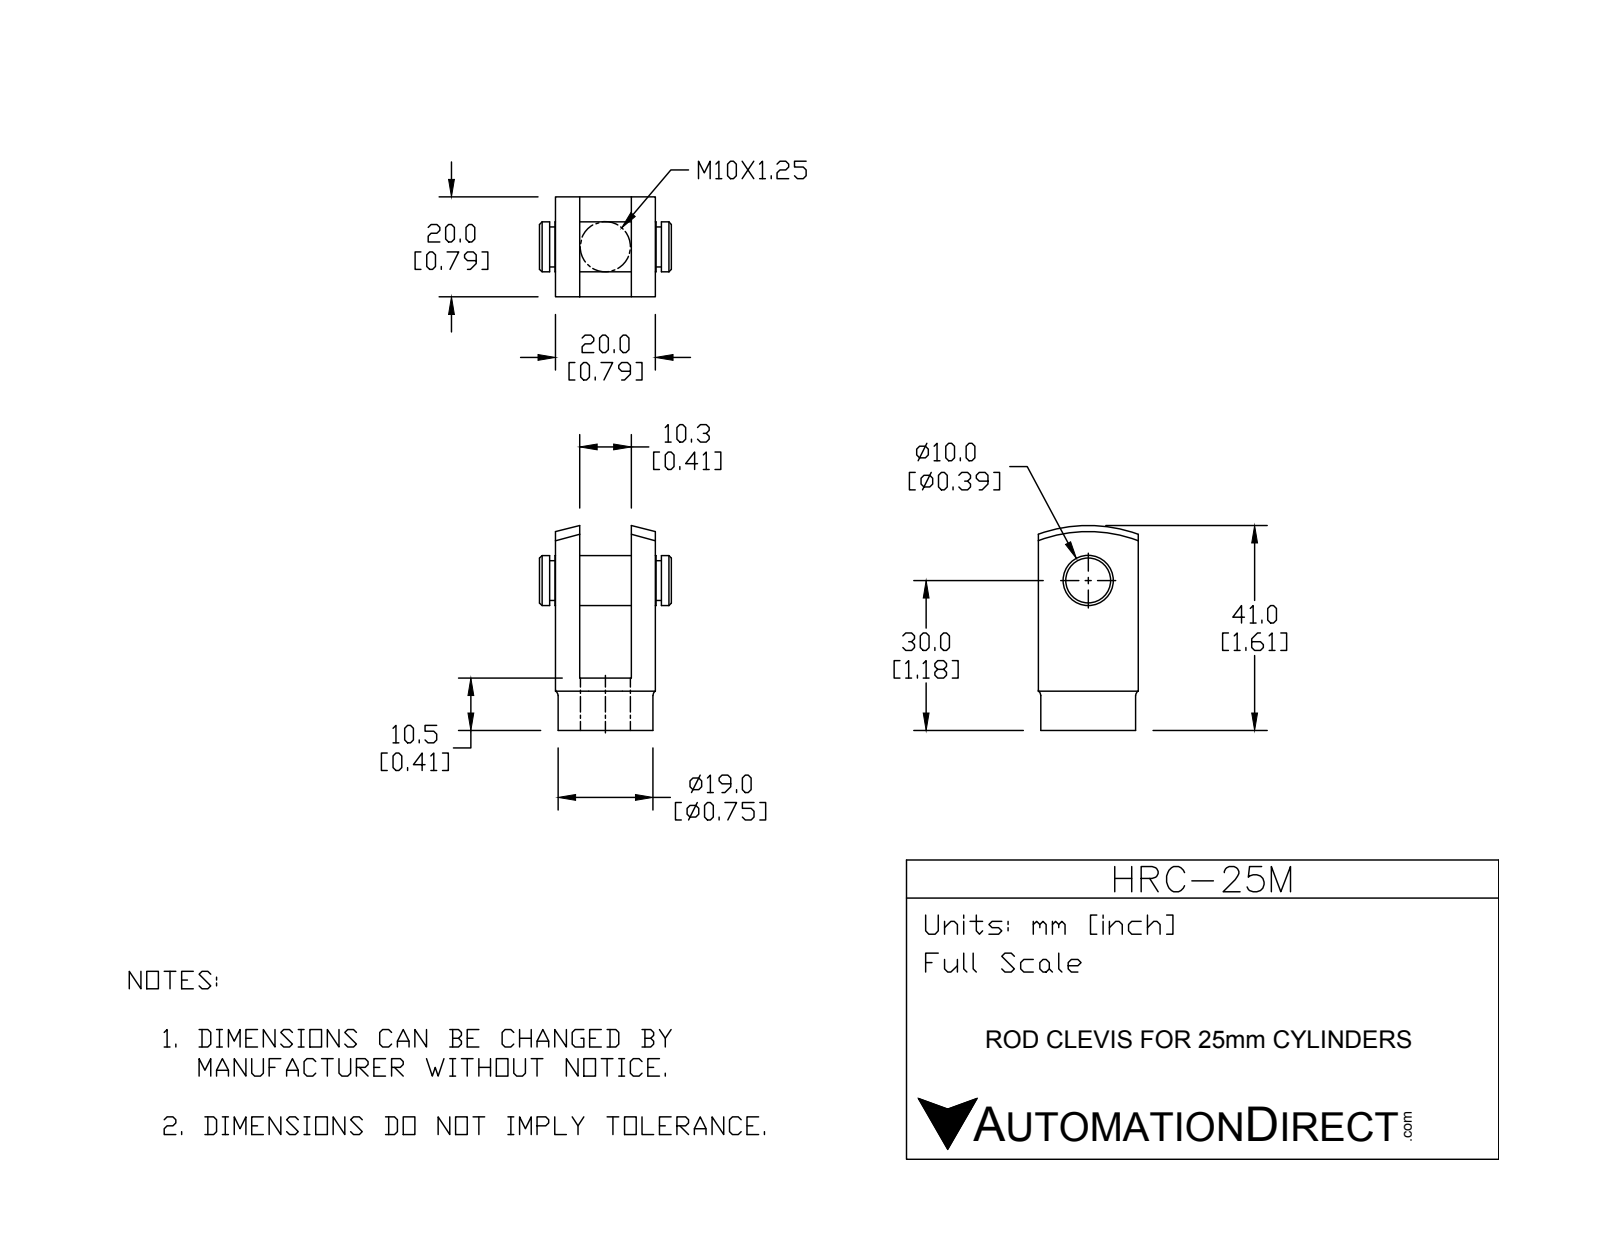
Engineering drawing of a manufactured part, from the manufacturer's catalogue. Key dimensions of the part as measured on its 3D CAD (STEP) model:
Part name (STEP PRODUCT): HRC-25M
STEP written by: SolidWorks 2015 (CONFIG_CONTROL_DESIGN)
Units: millimetres
Bodies: 2 solids, 54 faces (18 planar, 18 cylindrical, 18 other)
Overall size (bounding box): 41 × 26.4 × 20
Volume: 9 610 mm³ · Surface area: 5 557 mm²
Round holes (diameter × count): ⌀8.5 ×1
Round bosses / shafts (diameter × count): ⌀19 ×1, ⌀10 ×1, ⌀8 ×1
Main face-to-face distances: 4.85, 15.15, 20, 10.3, 3.2, 8.05, 18.35, 23.2, 10.5, 26.4
